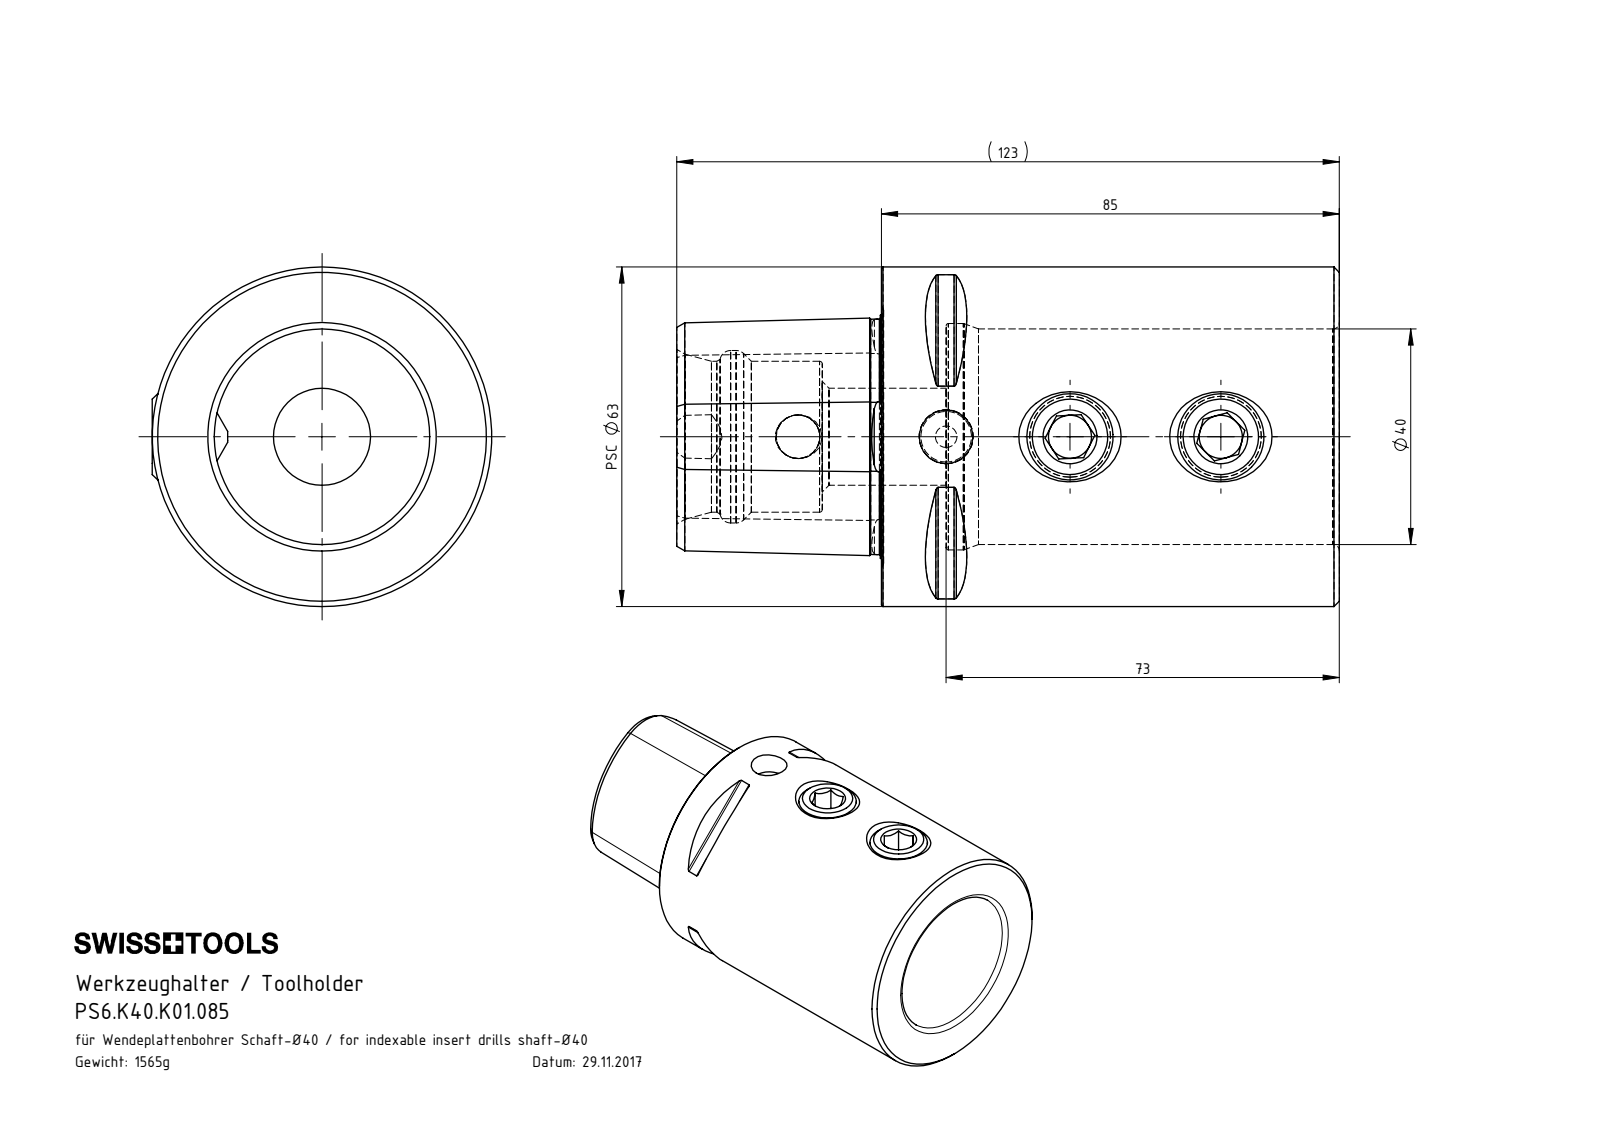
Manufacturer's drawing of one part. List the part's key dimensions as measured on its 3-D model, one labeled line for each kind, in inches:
Part name (STEP PRODUCT): PS6.K40.K01.085; K40-ER2.016.014_PreviewCfg; PS6-K40.K01.085_C; K40-ER1.016.012
STEP written by: SolidWorks 2017 (AUTOMOTIVE_DESIGN)
Units: inches
Bodies: 3 solids, 202 faces (50 planar, 45 cylindrical, 107 other)
Overall size (bounding box): 4.843 × 2.48 × 2.48
Volume: 12.08 in³ · Surface area: 68.45 in²
Round holes (diameter × count): ⌀0.315 ×2, ⌀0.591 ×2, ⌀0.319 ×1, ⌀0.394 ×1, ⌀0.63 ×1, ⌀0.709 ×1, ⌀1.102 ×1, ⌀1.26 ×1, ⌀1.575 ×1, ⌀1.654 ×1
Round bosses / shafts (diameter × count): ⌀0.63 ×2, ⌀2.48 ×1
Partial cylindrical surfaces — rounded edges, fillets, slot ends (radius × count): R0.02 ×8, R0.236 ×1
Main face-to-face distances: 3.346, 0.472, 2.874, 1.496, 1.969, 4.843, 0.98, 1.063, 0.433, 0.906
Hole centre spacings: 0.276, 0.63, 0.906, 1.083, 1.102, 1.378, 1.713, 1.988
